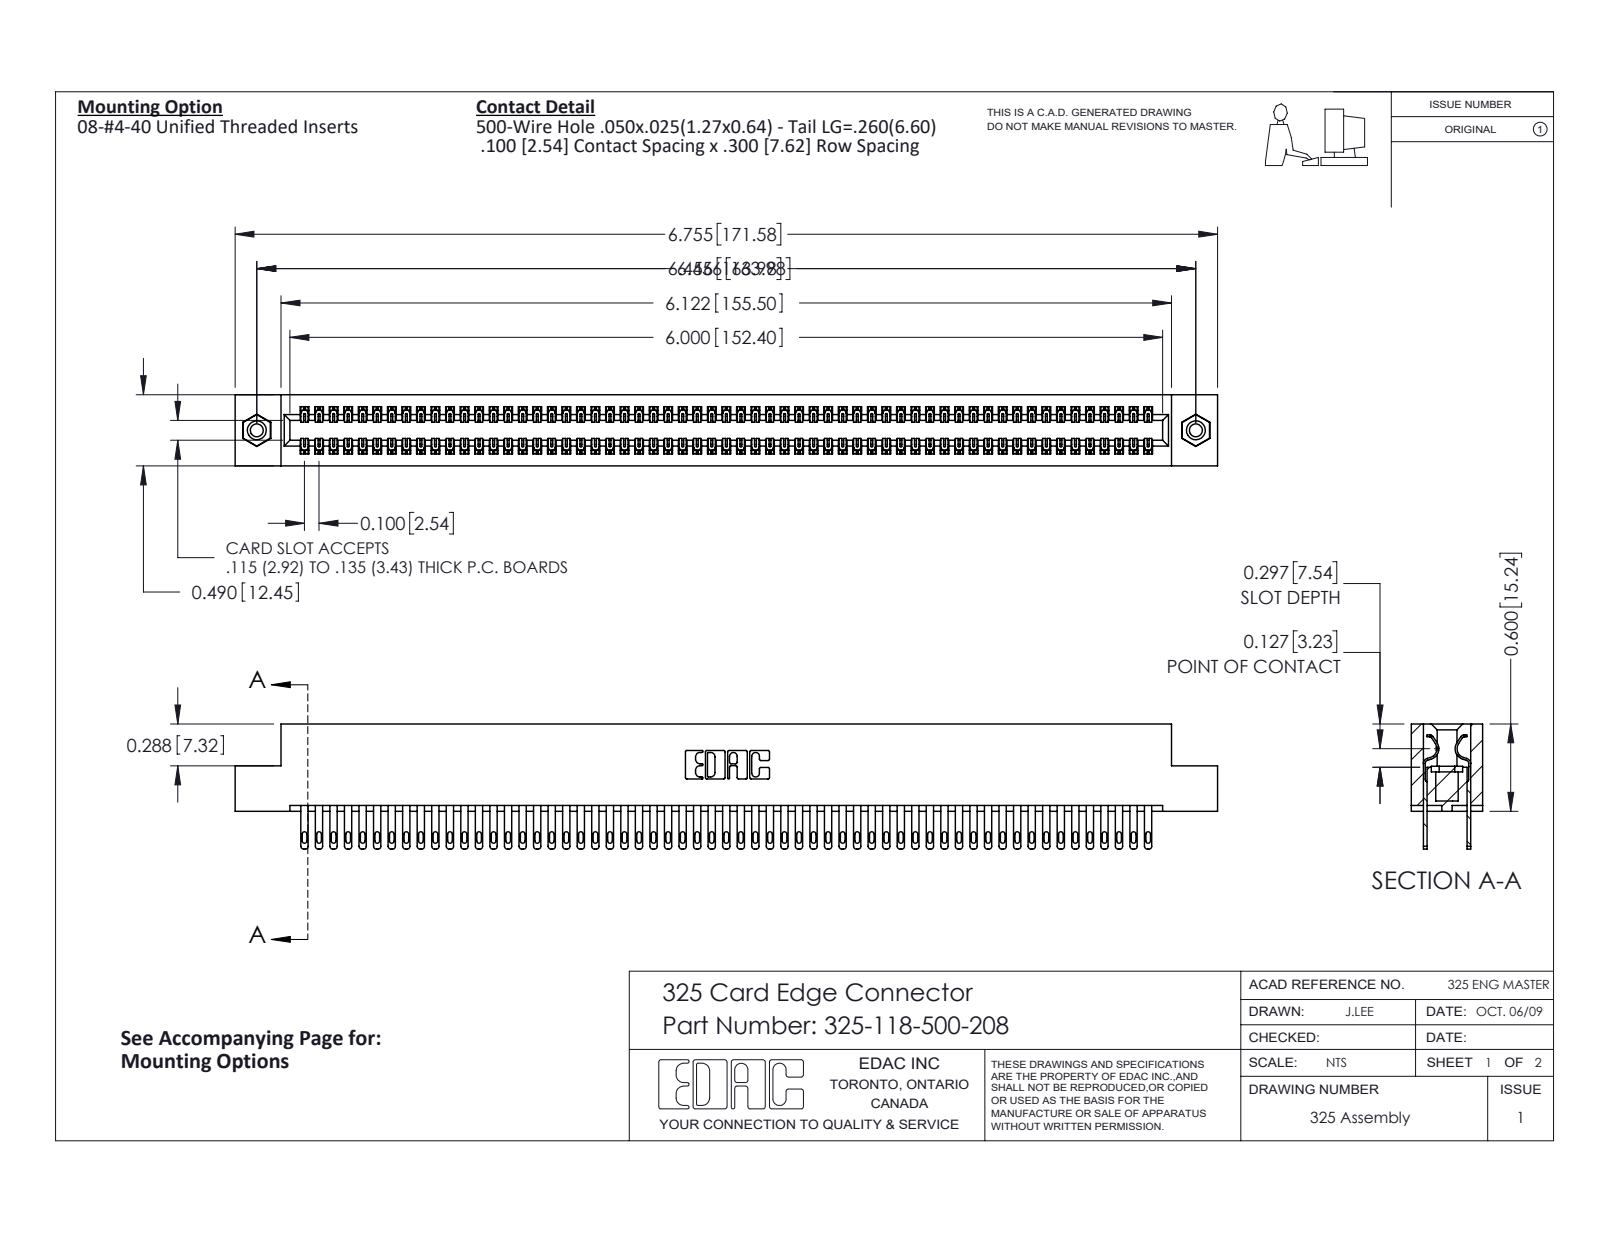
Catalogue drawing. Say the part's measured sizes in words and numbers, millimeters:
The part is named "325-292-001_325-293-100; 325-118-500-208; 325 Part_TI; 345-250-001_345-250-003-102". Its 3-D file was written by "SolidWorks 2016 (CONFIG_CONTROL_DESIGN)". It is 121 solids with 5838 faces: 3642 planar, 2180 cylindrical and 16 other. Overall it measures 171.6 by 21.8 by 12.4 millimeters. Its volume is 22 660 cubic millimeters and its surface area 29 070 square millimeters. Round holes: 2 of diameter 2.3, 2 of diameter 3.2, 2 of diameter 4.1. Round bosses or shafts: 2 of diameter 3.9. Partial cylindrical surfaces (rounded edges, fillets, slot ends): 177 of radius 0.2, 118 of radius 0.4, 118 of radius 0.5, 22 of radius 0.3, 6 of radius 0.2, 6 of radius 0.8, 3 of radius 0.7, 2 of radius 0.4. The main face-to-face distances are 2.1, 10.3, 7.6, 2.7, 9.7, 0.6, 12.4, 8.3, 7, 14.2. The hole center spacings are 164.
